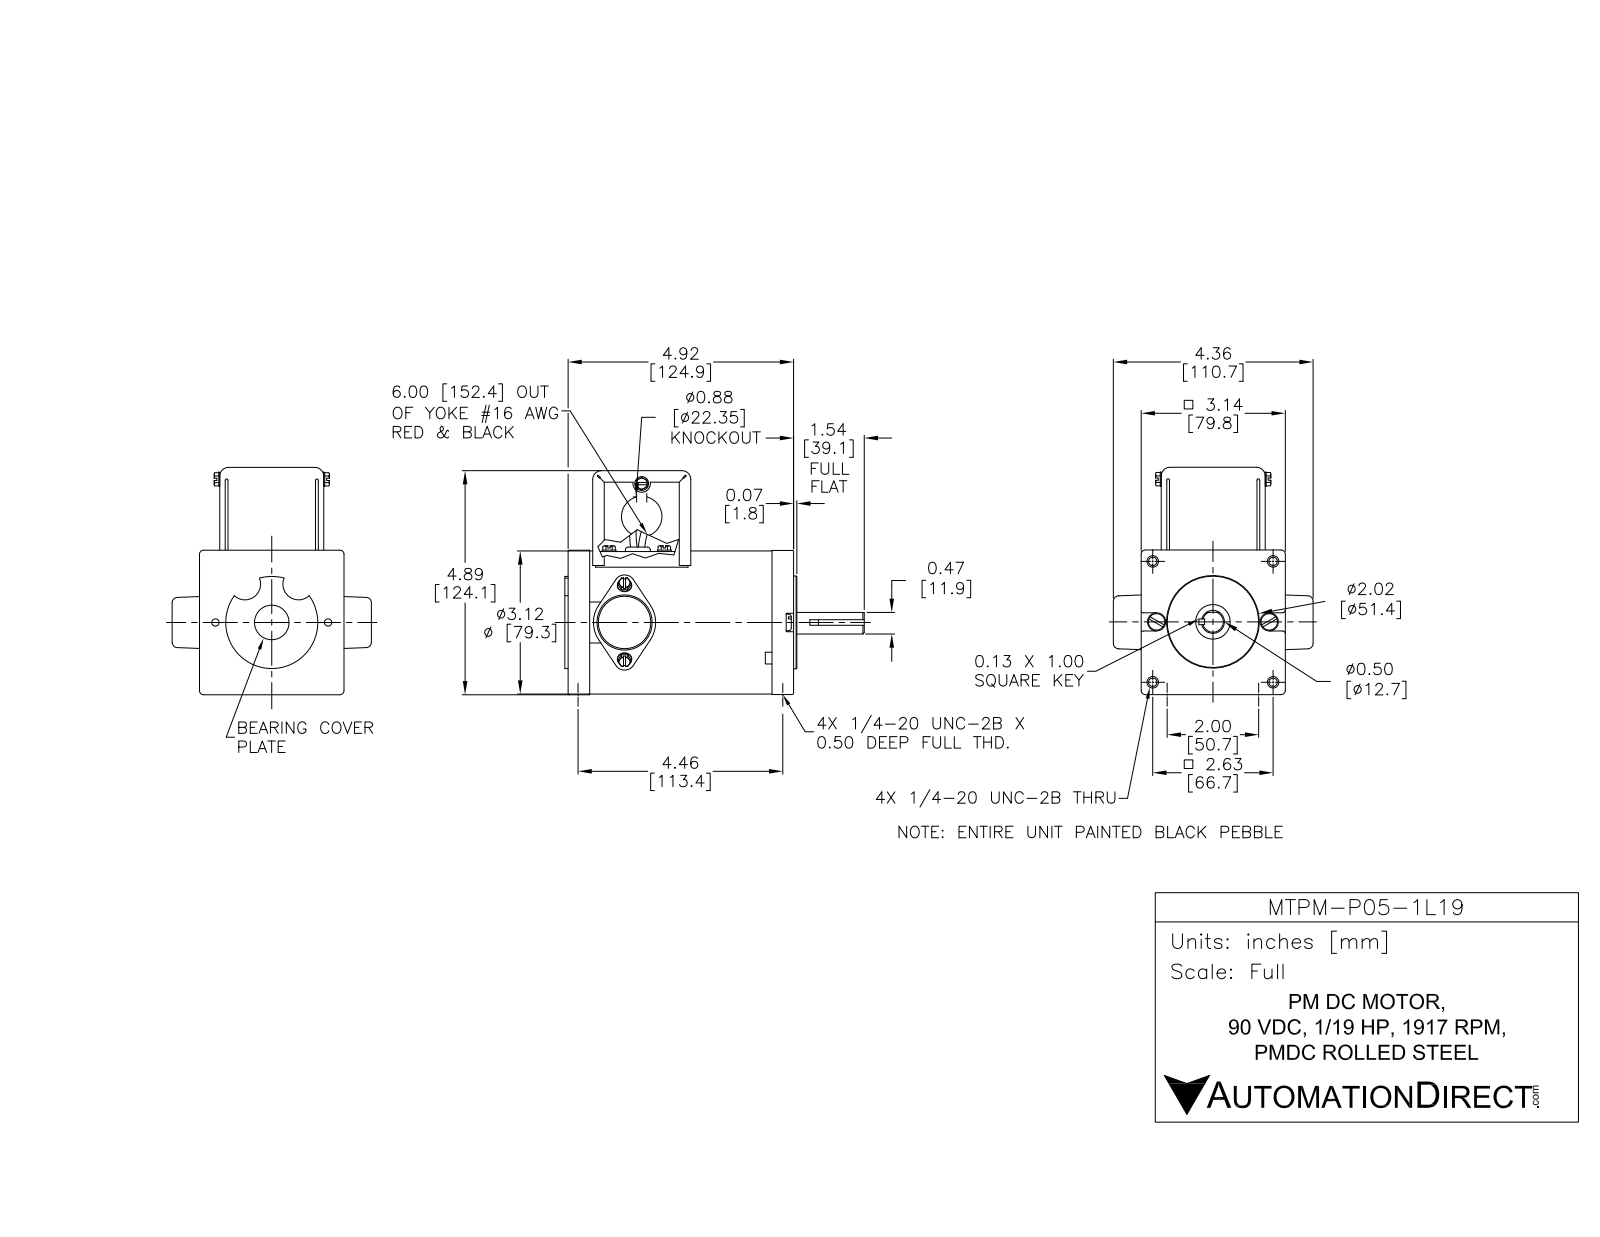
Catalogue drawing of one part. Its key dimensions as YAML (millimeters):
part_name: "MTPM-P05-1L19"
step_written_by: "SolidWorks 2017 (AUTOMOTIVE_DESIGN)"
units: millimeters
bodies: {solids: 28, faces: 410, planar: 271, cylindrical: 114, other: 25}
overall_size: [165.6, 125.6, 111.5]
volume: 198800
surface_area: 149500
round_holes:
  - {diameter: 3.2, count: 4}
  - {diameter: 5, count: 2}
  - {diameter: 6.4, count: 1}
  - {diameter: 7.6, count: 1}
  - {diameter: 9.5, count: 1}
  - {diameter: 12.7, count: 1}
  - {diameter: 31.1, count: 1}
  - {diameter: 51.3, count: 1}
  - {diameter: 76.2, count: 1}
  - {diameter: 79.4, count: 1}
round_bosses_or_shafts:
  - {diameter: 7.6, count: 4}
  - {diameter: 3.2, count: 2}
  - {diameter: 2.5, count: 2}
  - {diameter: 15.9, count: 1}
partial_cylinders:
  - {radius: 4.9, count: 4}
  - {radius: 5.9, count: 4}
  - {radius: 4, count: 2}
  - {radius: 8.7, count: 2}
  - {radius: 3.8, count: 1}
  - {radius: 15.6, count: 1}
  - {radius: 16.9, count: 1}
  - {radius: 17.2, count: 1}
face_to_face_distances: [0.8, 6.4, 118.5, 1.6, 54.2, 112.1, 52, 2.4, 124.8, 55.8]
hole_center_spacings: [33.5, 47.2, 66.8, 72.8, 31.2, 94.5, 62.5, 78.3]
